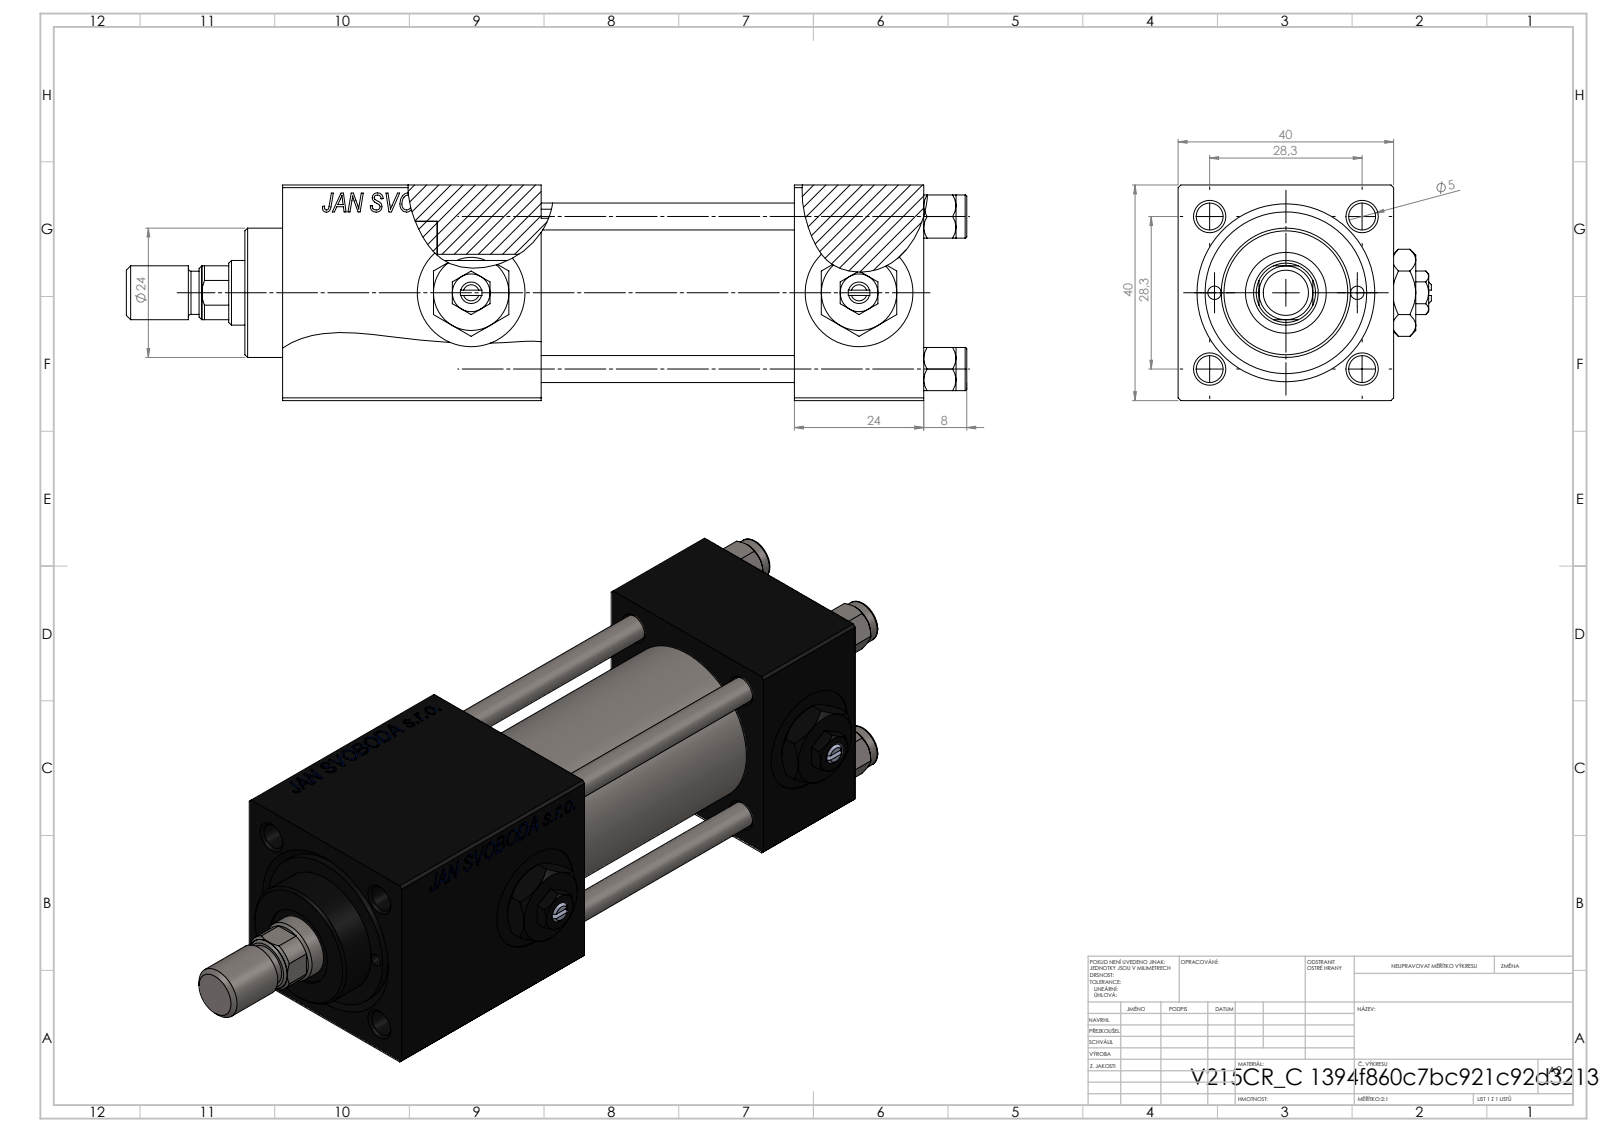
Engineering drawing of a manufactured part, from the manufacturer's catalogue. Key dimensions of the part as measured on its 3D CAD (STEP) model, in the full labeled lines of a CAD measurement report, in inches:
Part name (STEP PRODUCT): V215CR_C_Body; NUT_M5_C; V215CR_C_TYCINKA; V215CR_VCP_C (+3 more)
STEP written by: SolidWorks 2019 (CONFIG_CONTROL_DESIGN)
Units: inches
Bodies: 14 solids, 1268 faces (578 planar, 106 cylindrical, 584 other)
Overall size (bounding box): 6.142 × 1.85 × 1.575
Volume: 8.663 in³ · Surface area: 88.19 in²
Round holes (diameter × count): ⌀0.197 ×4, ⌀0.787 ×3, ⌀0.098 ×2, ⌀0.276 ×2, ⌀0.518 ×2, ⌀0.256 ×1, ⌀0.472 ×1, ⌀0.591 ×1, ⌀0.984 ×1, ⌀1.181 ×1
Round bosses / shafts (diameter × count): ⌀0.315 ×5, ⌀1.22 ×1, ⌀0.945 ×1, ⌀0.394 ×1
Partial cylindrical surfaces — rounded edges, fillets, slot ends (radius × count): R0.217 ×1
Main face-to-face distances: 1.575, 0.945, 1.567, 1.89, 3.555, 2.61, 2.795, 1.85, 0.76, 3.74
Hole centre spacings: 0.558, 0.788, 1.114, 1.214, 0.522, 1.576, 1.043, 2.835
